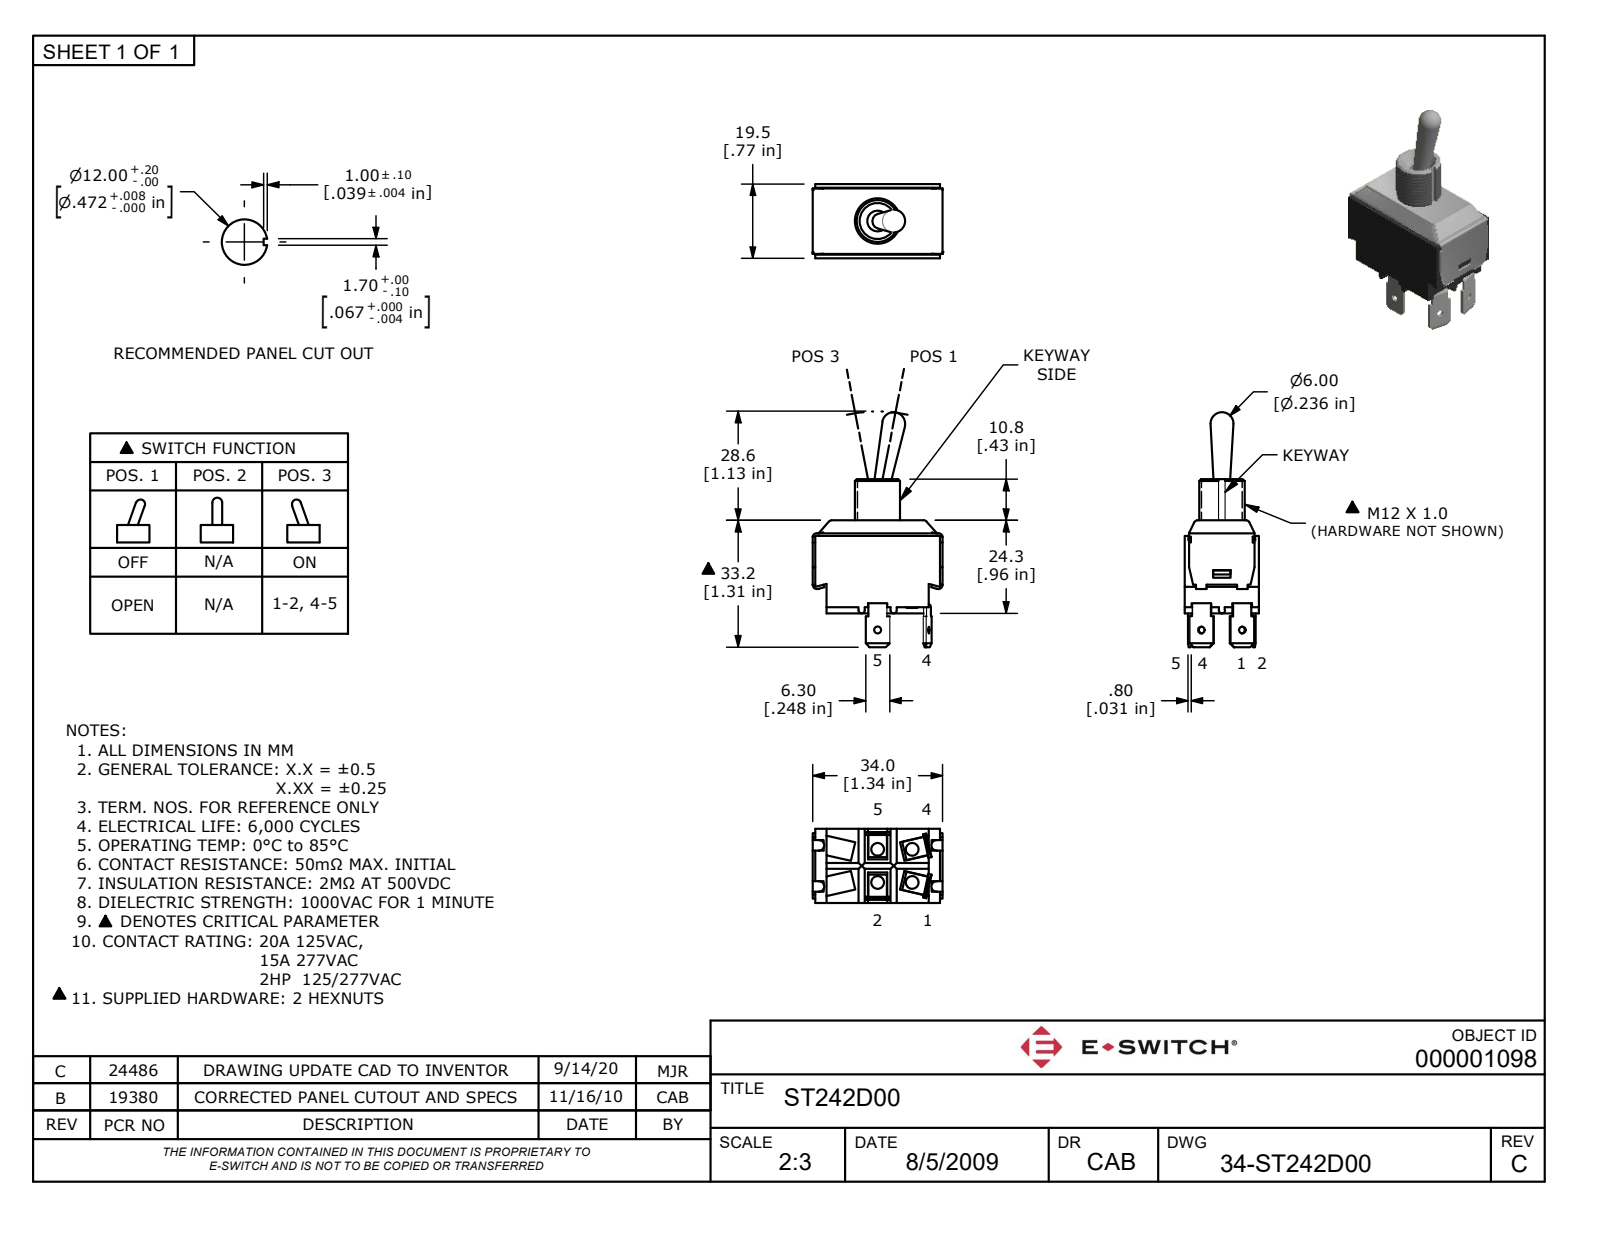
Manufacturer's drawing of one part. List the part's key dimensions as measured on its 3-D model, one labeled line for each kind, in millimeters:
Part name (STEP PRODUCT): ST242D00
STEP written by: Autodesk Inventor 2022 (AUTOMOTIVE_DESIGN)
Units: millimetres
Bodies: 1 solid, 332 faces (233 planar, 65 cylindrical, 34 other)
Overall size (bounding box): 61.5 × 34 × 19.5
Volume: 14 968 mm³ · Surface area: 5 535 mm²
Round holes (diameter × count): ⌀2 ×4, ⌀1.8 ×3, ⌀4 ×1, ⌀5.4 ×1
Round bosses / shafts (diameter × count): ⌀11.91 ×1
Partial cylindrical surfaces — rounded edges, fillets, slot ends (radius × count): R1 ×10, R0.3 ×6, R1.1 ×6, R0.25 ×4, R1.4 ×4, R0.8 ×3, R0.2 ×2, R0.6 ×2
Main face-to-face distances: 19.5, 0.8, 3.6, 30.4, 34, 22.7, 18.6, 0.9, 1.7, 0.65
Hole centre spacings: 4.35, 8.7, 9, 10, 12.52
